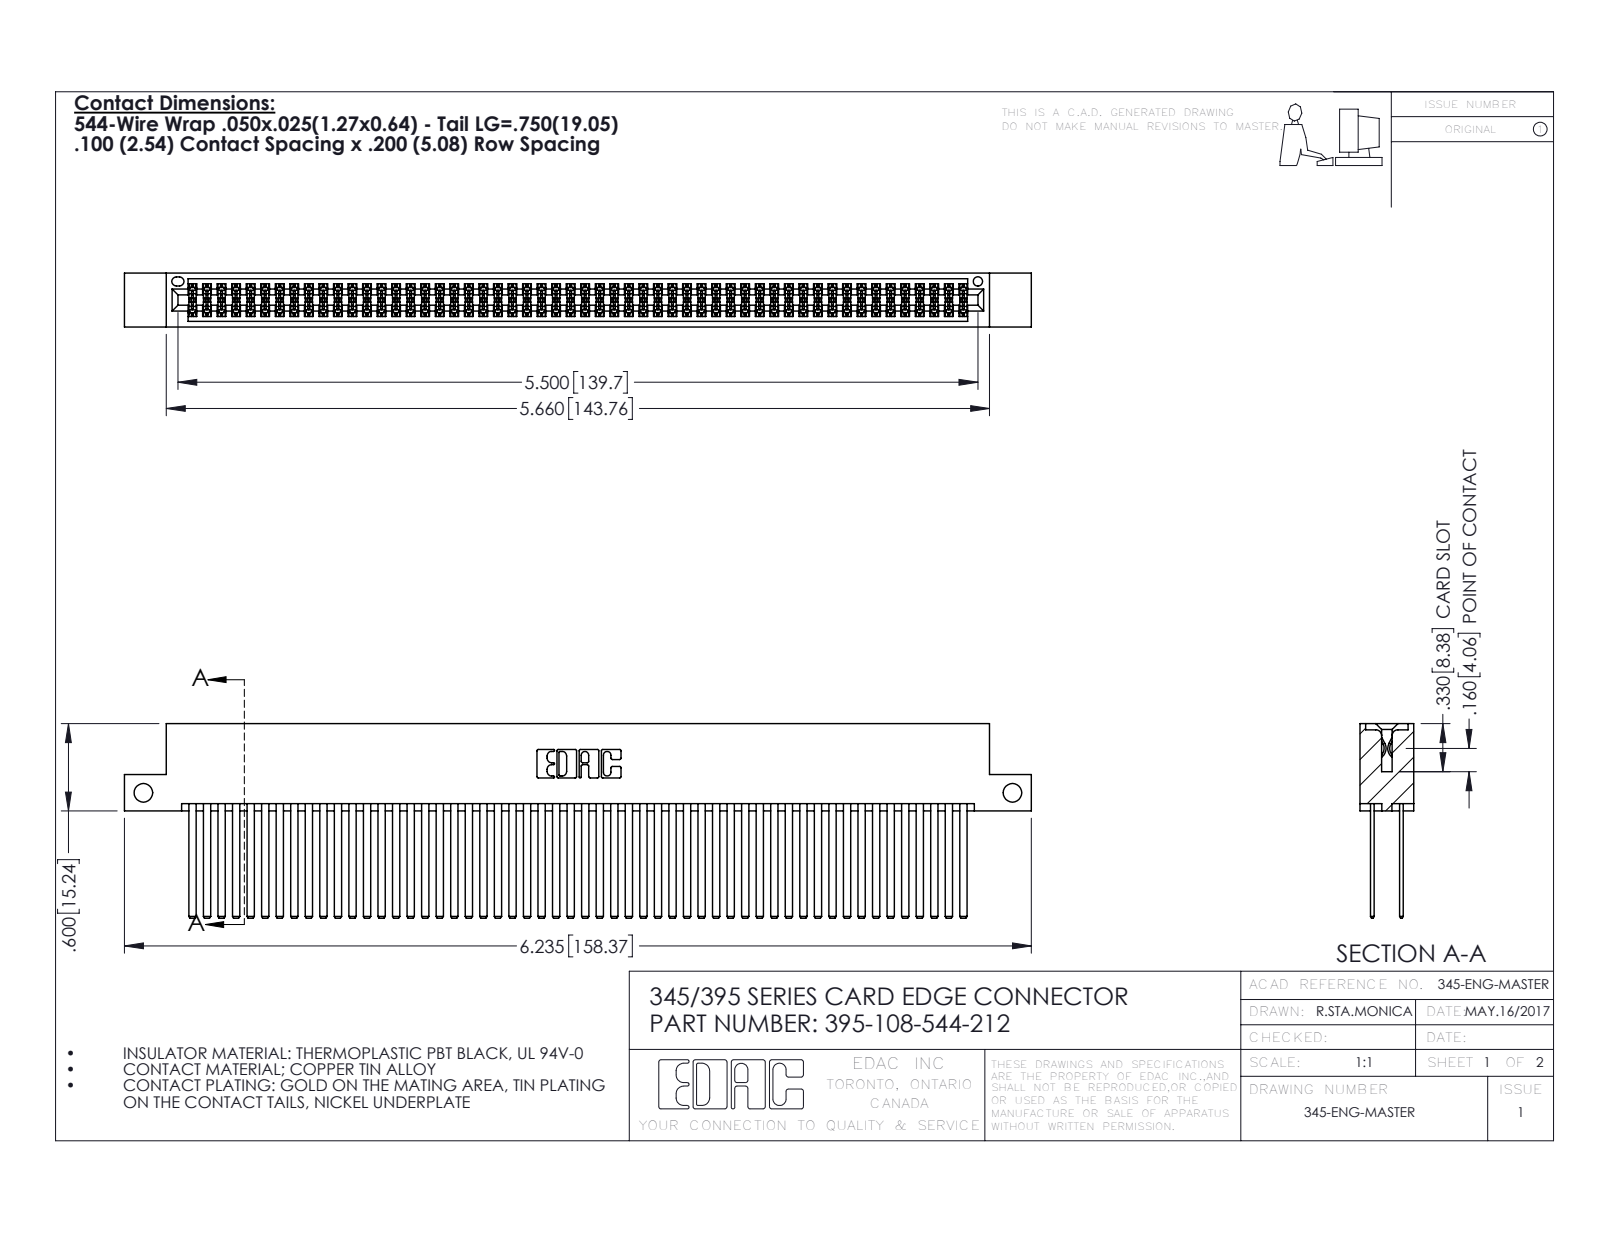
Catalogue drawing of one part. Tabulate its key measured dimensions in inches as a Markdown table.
| quantity | value |
| --- | --- |
| part name | 345 Part_Flush Mounting Lugs - Side Mount; 395-108-544-212; 345-292-001_345-293-144 |
| STEP written by | SolidWorks 2016 (CONFIG_CONTROL_DESIGN) |
| units | inches |
| bodies | 109 solids, 4878 faces (3212 planar, 1666 cylindrical, 0 other) |
| overall size | 6.235 × 1.337 × 0.37 |
| volume | 1.033 in³ |
| surface area | 45.8 in² |
| round holes (diameter × count) | 0.128 × 2, 0.064 × 1 |
| partial cylindrical surfaces (radius × count) | 0.006 × 162, 0.01 × 22, 0.007 × 6, 0.031 × 6, 0.026 × 3, 0.014 × 2, 0.019 × 2, 0.022 × 2 |
| main face-to-face distances | 0.2, 0.025, 0.298, 0.072, 0.098, 0.272, 0.225, 0.175, 0.37, 0.05 |
| hole center spacings | 5.975 |
